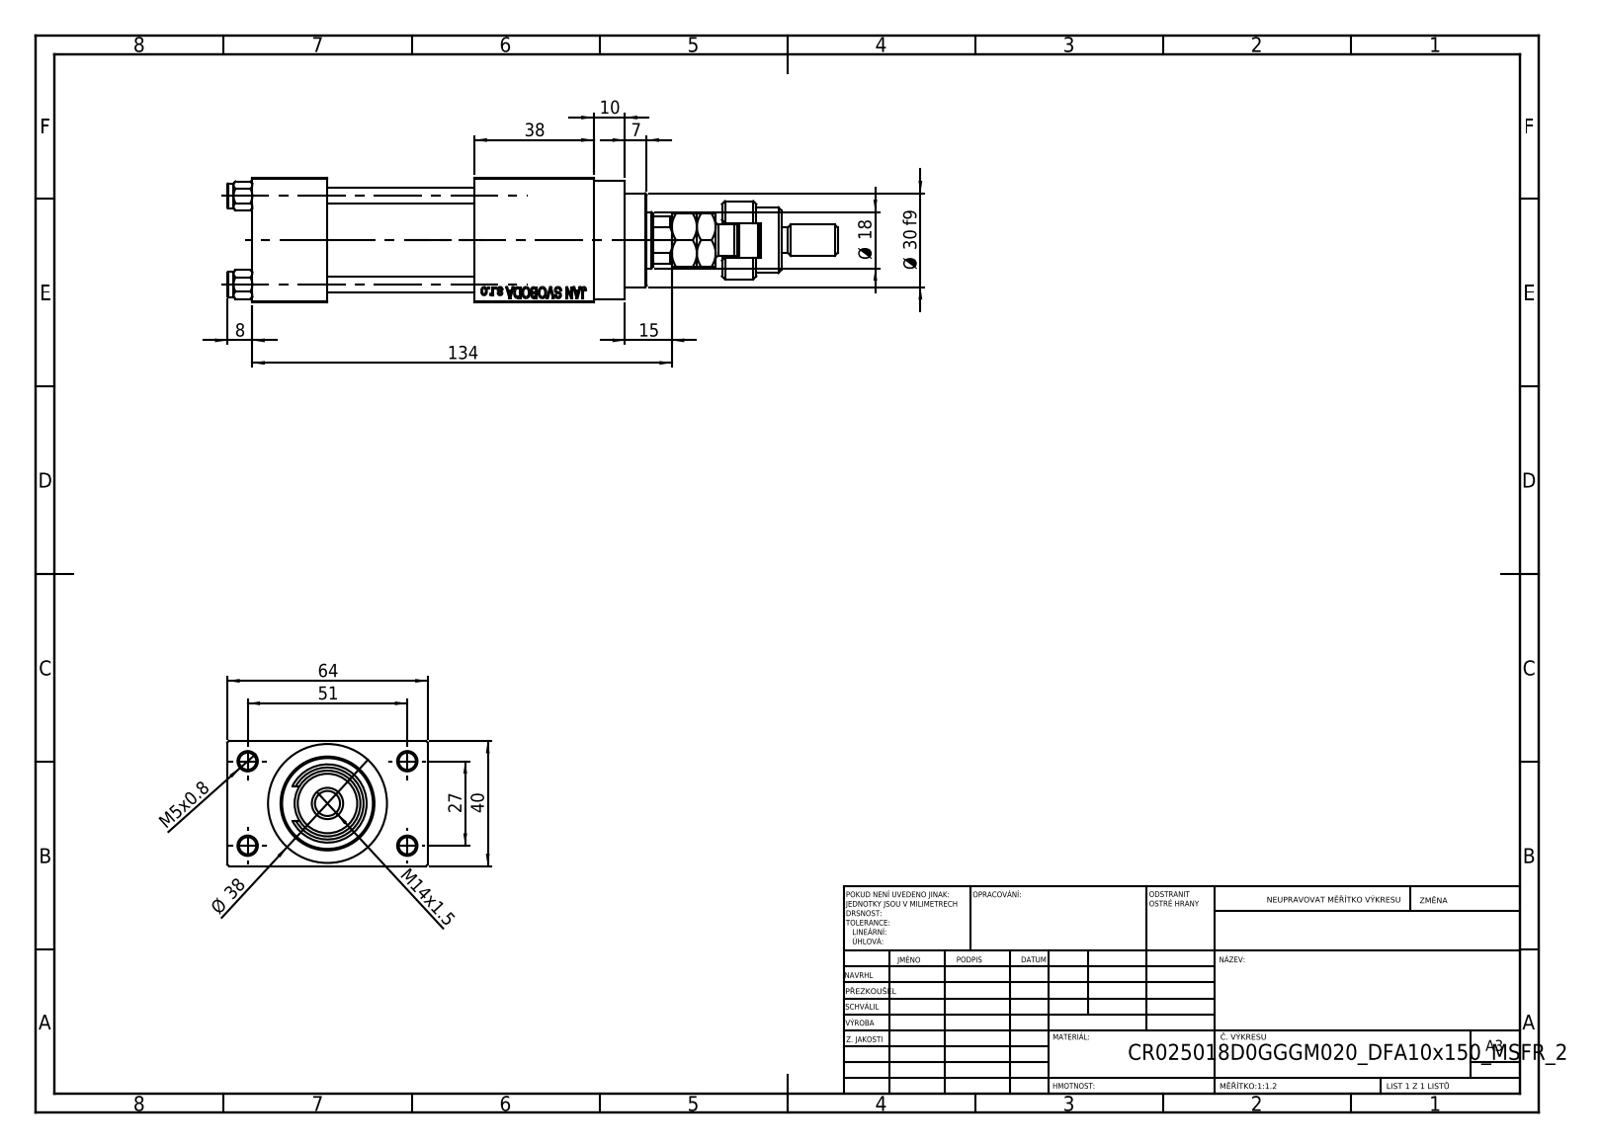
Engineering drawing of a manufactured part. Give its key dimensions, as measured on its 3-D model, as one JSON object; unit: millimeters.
{"part_name": "V215CR_D_Body; V215CR_VCP_D; FEMALE_PART_FOR_DFA; NUT_M5_D (+3 more)", "step_written_by": "SolidWorks 2019 (CONFIG_CONTROL_DESIGN)", "units": "millimeters", "bodies": {"solids": 13, "faces": 1185, "planar": 523, "cylindrical": 100, "other": 562}, "overall_size": [195, 64, 40], "volume_mm3": 192578, "surface_area_mm2": 69659, "round_holes": [[5, 4], [5.5, 4], [20, 3], [7, 2], [13.16, 2], [8.5, 1], [18, 1], [21, 1], [30, 1]], "round_bosses_or_shafts": [[8, 5], [38, 1], [31, 1], [25, 1], [16, 1], [10, 1]], "partial_cylinders_radius": [[5.5, 1], [8.5, 1], [8.75, 1]], "face_to_face_distances": [40, 12, 52, 24, 47, 64, 71, 38, 109, 85], "hole_center_spacings": [11.37, 20.01, 28.3, 28.85, 29.89, 39.66, 48.34, 27]}
